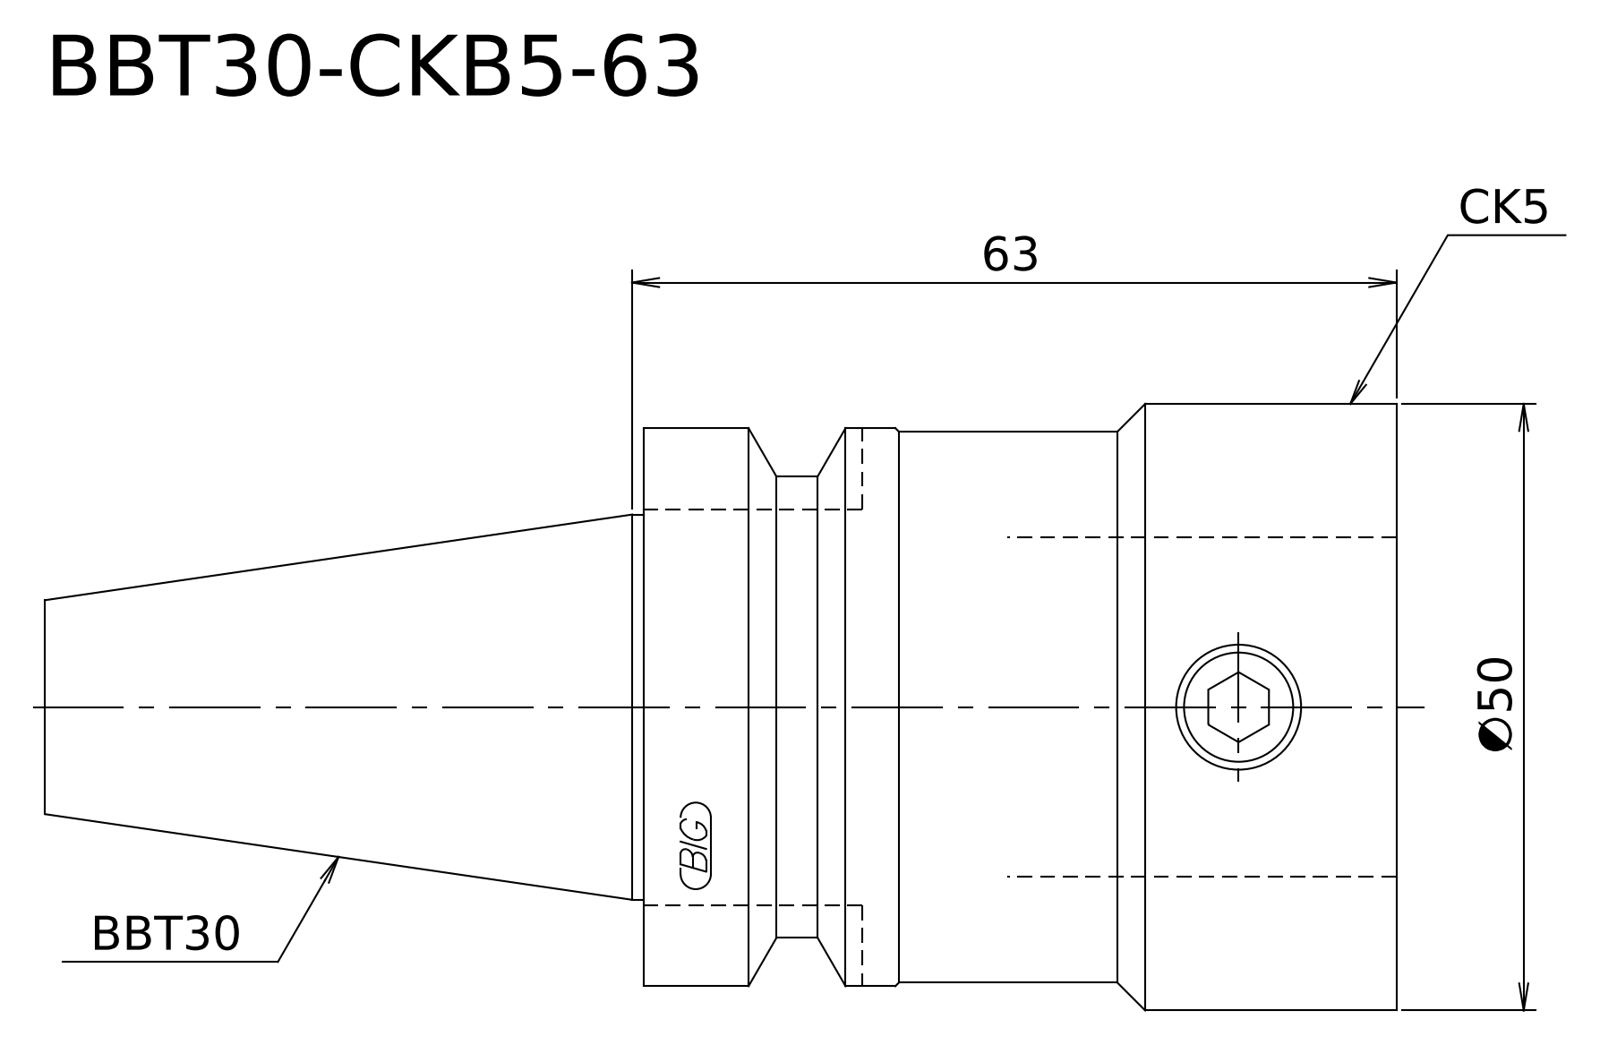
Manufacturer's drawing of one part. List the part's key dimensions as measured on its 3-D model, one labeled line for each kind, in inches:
STEP written by: Kubotek KeyCreator V8.5.1 (14335) (CONFIG_CONTROL_DESIGN)
Units: inches
Bodies: 1 solid, 14 faces (3 planar, 6 cylindrical, 5 other)
Overall size (bounding box): 4.386 × 1.969 × 1.969
Volume: 7.954 in³ · Surface area: 26.04 in²
Round bosses / shafts (diameter × count): ⌀1.969 ×1, ⌀1.811 ×1, ⌀1.787 ×1, ⌀1.496 ×1, ⌀1.25 ×1
Main face-to-face distances: 2.441, 4.386, 1.945
